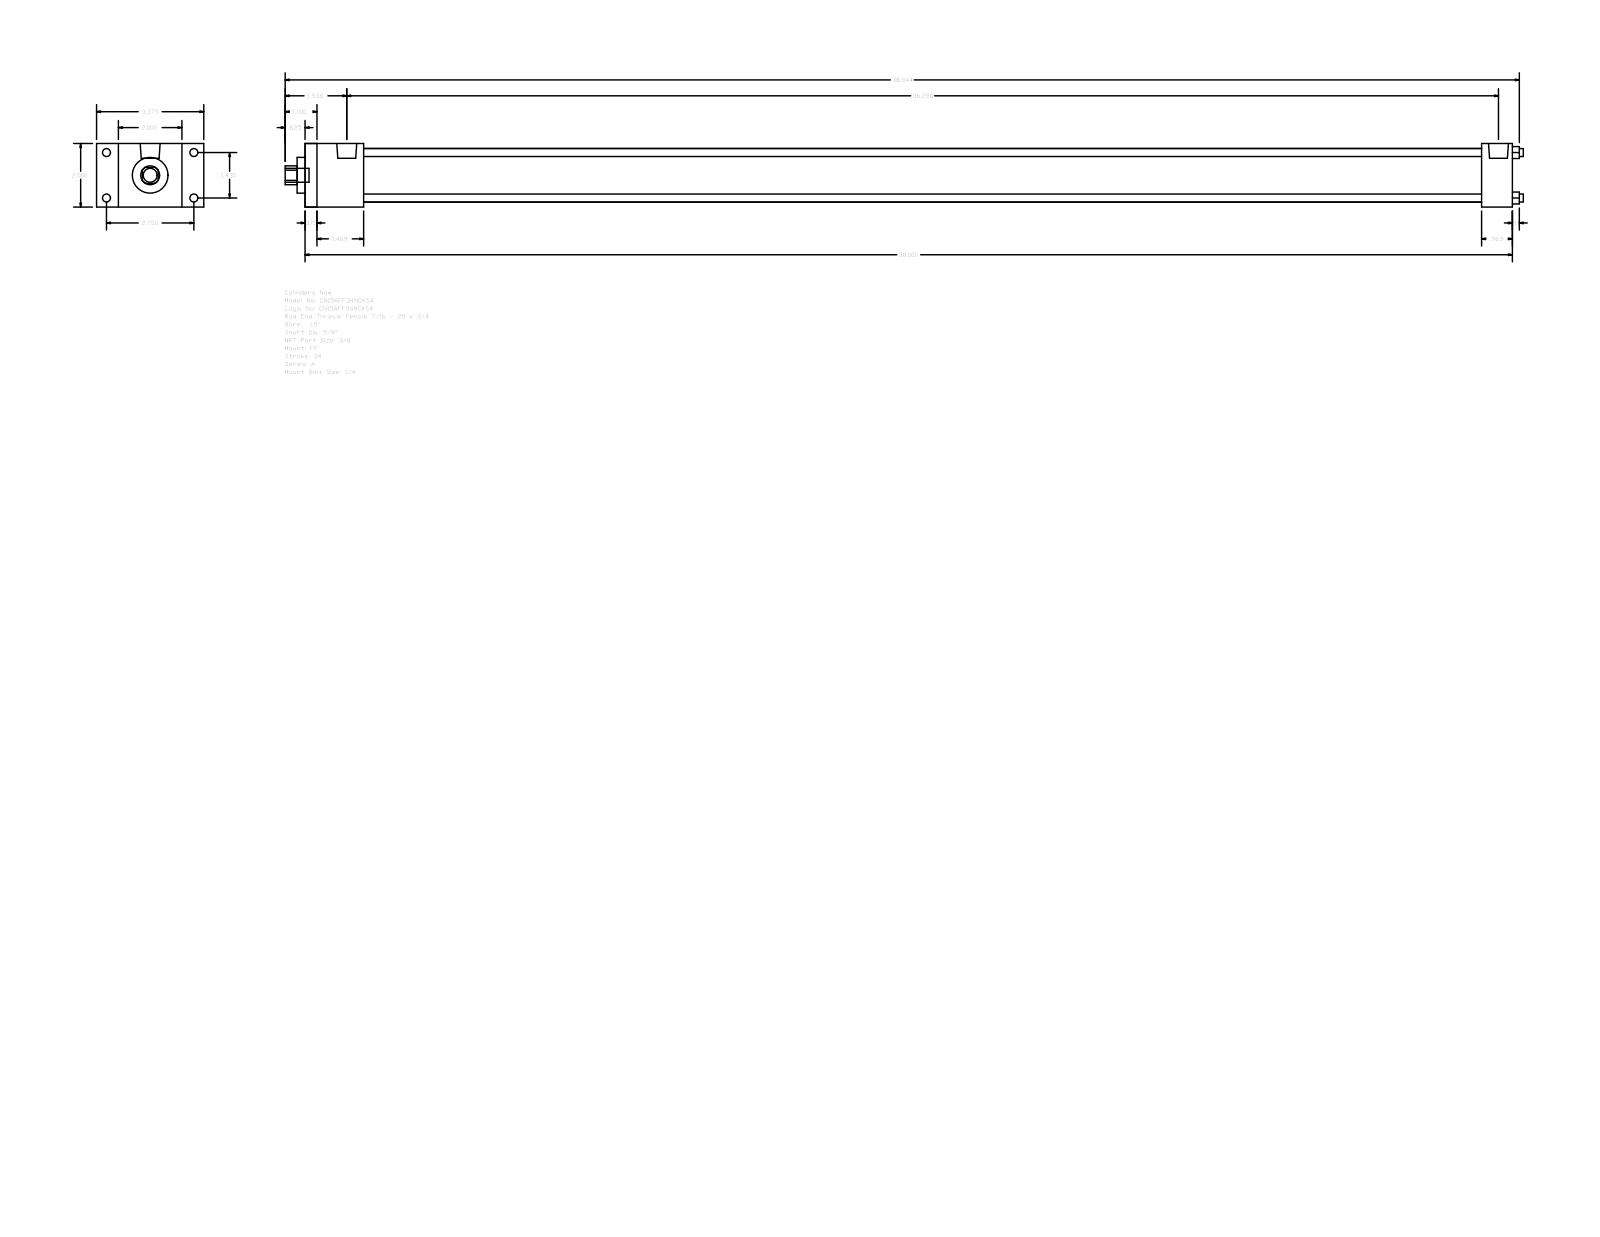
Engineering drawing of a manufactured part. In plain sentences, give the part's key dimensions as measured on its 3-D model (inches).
The part is named "A_FF__0150_0.625". Its 3-D file was written by "GSSL Pune (CONFIG_CONTROL_DESIGN)". It is 0 solids with 92 faces: 64 planar, 28 cylindrical and 0 other. Overall it measures 38.969 by 3.375 by 2 inches. Round holes: 4 of diameter 0.25, 1 of diameter 0.625, 1 of diameter 1.125, 1 of diameter 1.69. Round bosses or shafts: 4 of diameter 0.25, 4 of diameter 0.219, 2 of diameter 0.627, 1 of diameter 0.437. Partial cylindrical surfaces (rounded edges, fillets, slot ends): 1 of radius 0.297. The main face-to-face distances are 2, 38, 0.375, 37.625, 1.844, 37.031, 1.469, 36.656, 35.187, 36.156. The hole center spacings are 1.011, 1.43, 2.022.
